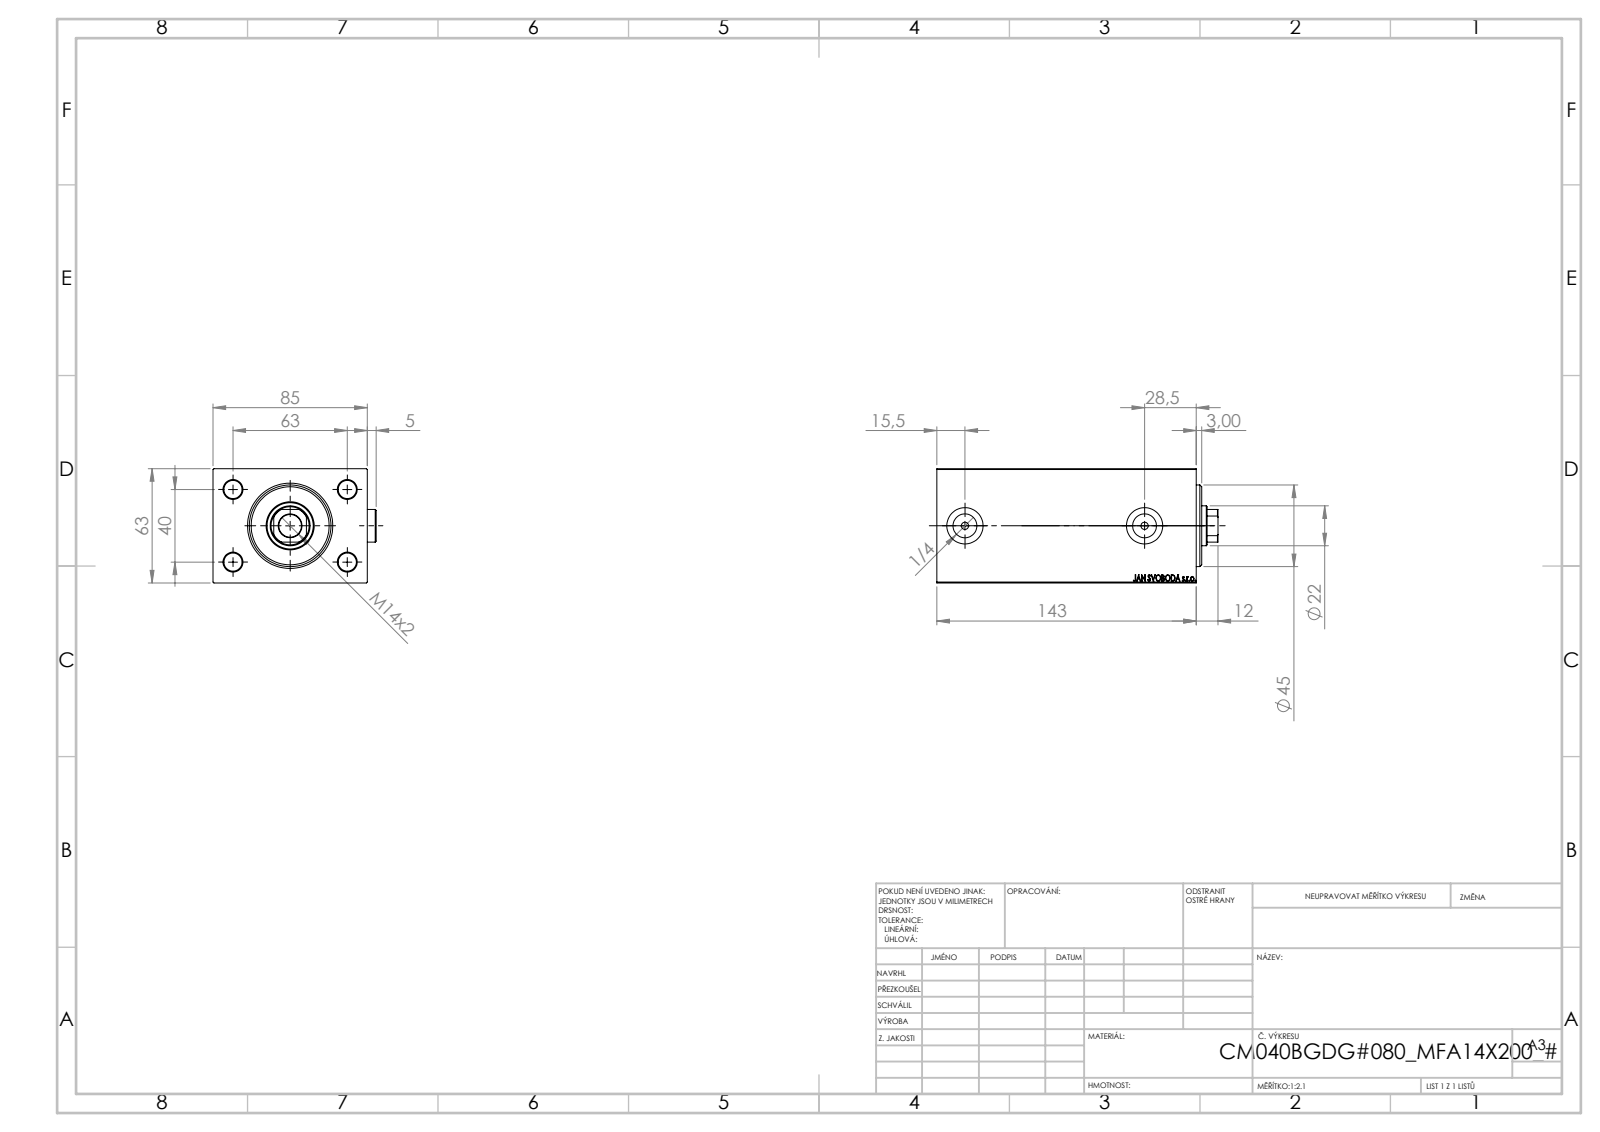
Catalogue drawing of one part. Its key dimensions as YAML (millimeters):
part_name: "V450CM_VC_B; Zatka_OIL_PORT; V450CM_B_VCP; V450CM_B_Body"
step_written_by: "SolidWorks 2019 (CONFIG_CONTROL_DESIGN)"
units: millimeters
bodies: {solids: 5, faces: 935, planar: 435, cylindrical: 70, other: 430}
overall_size: [155, 89.9, 63]
volume: 681846
surface_area: 99551
round_holes:
  - {diameter: 10, count: 4}
  - {diameter: 4, count: 2}
  - {diameter: 13.16, count: 2}
  - {diameter: 20, count: 2}
  - {diameter: 12.5, count: 1}
  - {diameter: 22, count: 1}
  - {diameter: 25.5, count: 1}
  - {diameter: 26.5, count: 1}
  - {diameter: 40, count: 1}
  - {diameter: 42, count: 1}
  - {diameter: 45, count: 1}
round_bosses_or_shafts:
  - {diameter: 18, count: 2}
partial_cylinders:
  - {radius: 10.5, count: 1}
face_to_face_distances: [63, 85, 12, 131, 143, 84.9, 119, 3, 15, 134]
hole_center_spacings: [37.31, 40, 63, 74.63, 99]
